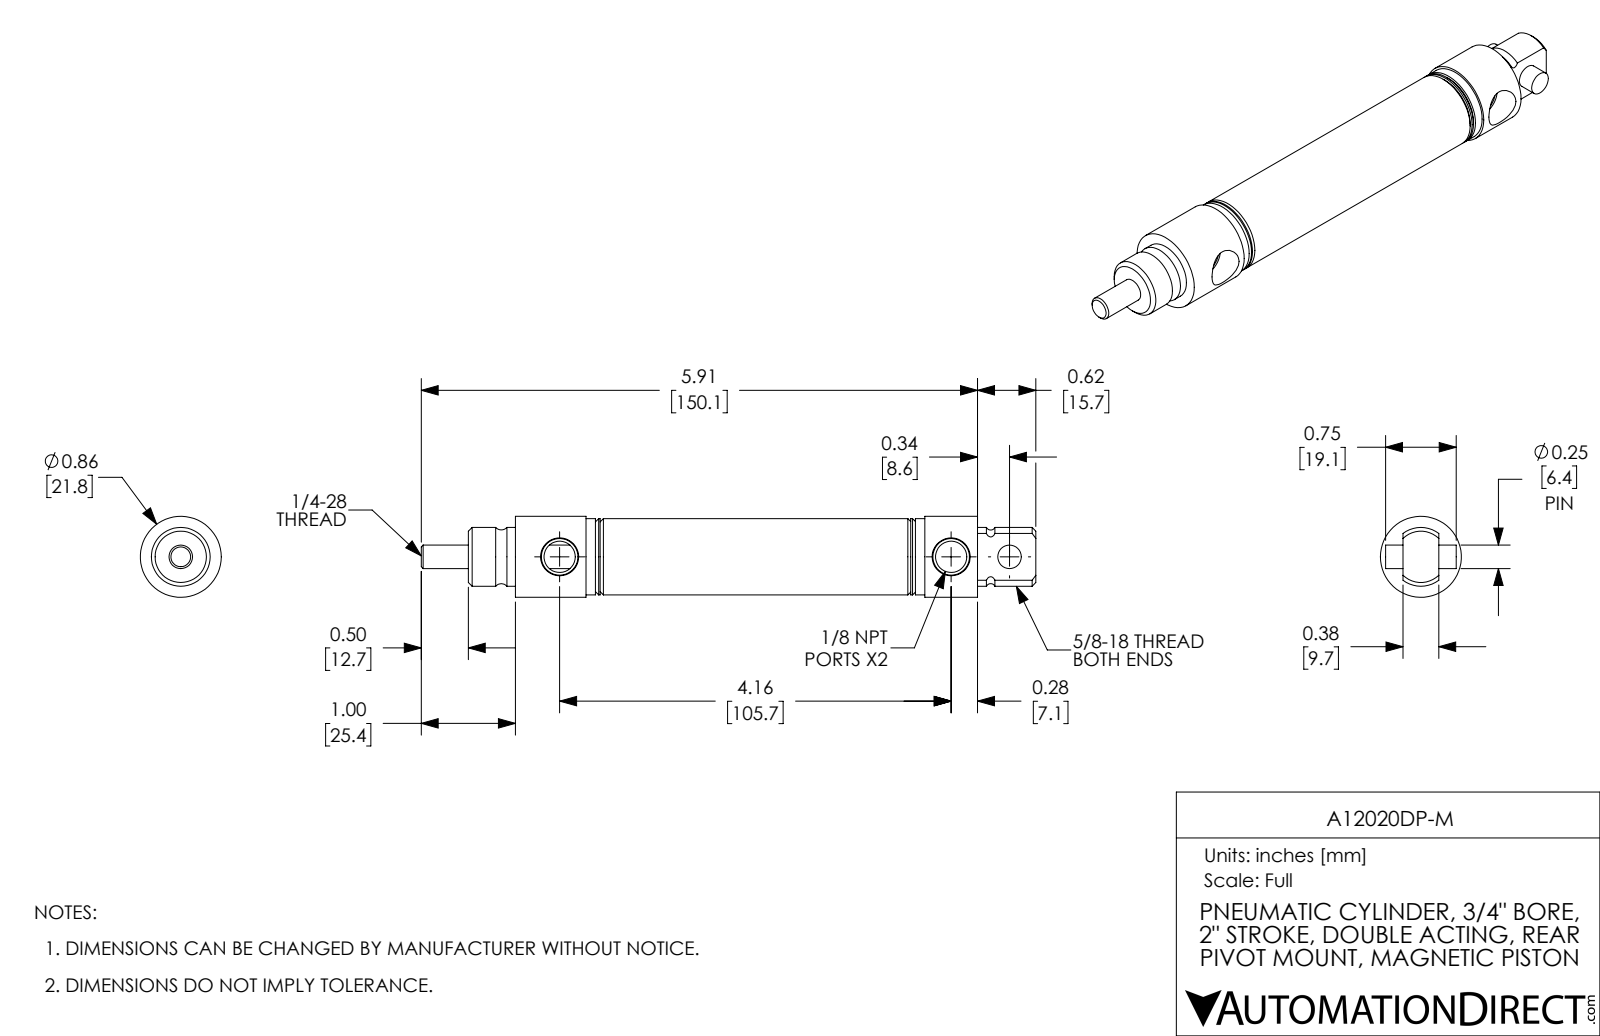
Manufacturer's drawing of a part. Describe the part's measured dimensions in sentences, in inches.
The part is named "A12020DP-M-MainBody; A12020DP-M-Rod; A12020DP-M-PIN; A12020DP-M". Its 3-D file was written by "SolidWorks 2017 (AUTOMOTIVE_DESIGN)". It is 3 solids with 91 faces: 21 planar, 38 cylindrical and 32 other. Overall it measures 6.53 by 0.86 by 0.86 inches. Its volume is 2.061 cubic inches and its surface area 31.47 square inches. Round holes: 2 of diameter 0.25, 2 of diameter 0.332, 1 of diameter 0.75. Round bosses or shafts: 1 of diameter 0.86, 1 of diameter 0.81, 1 of diameter 0.625. The main face-to-face distances are 0.5, 3.705, 2.5, 2, 1.205, 1.705, 3.705, 4.91, 3.205, 1.205. The hole center spacings are 0.62, 4.16, 4.78.
